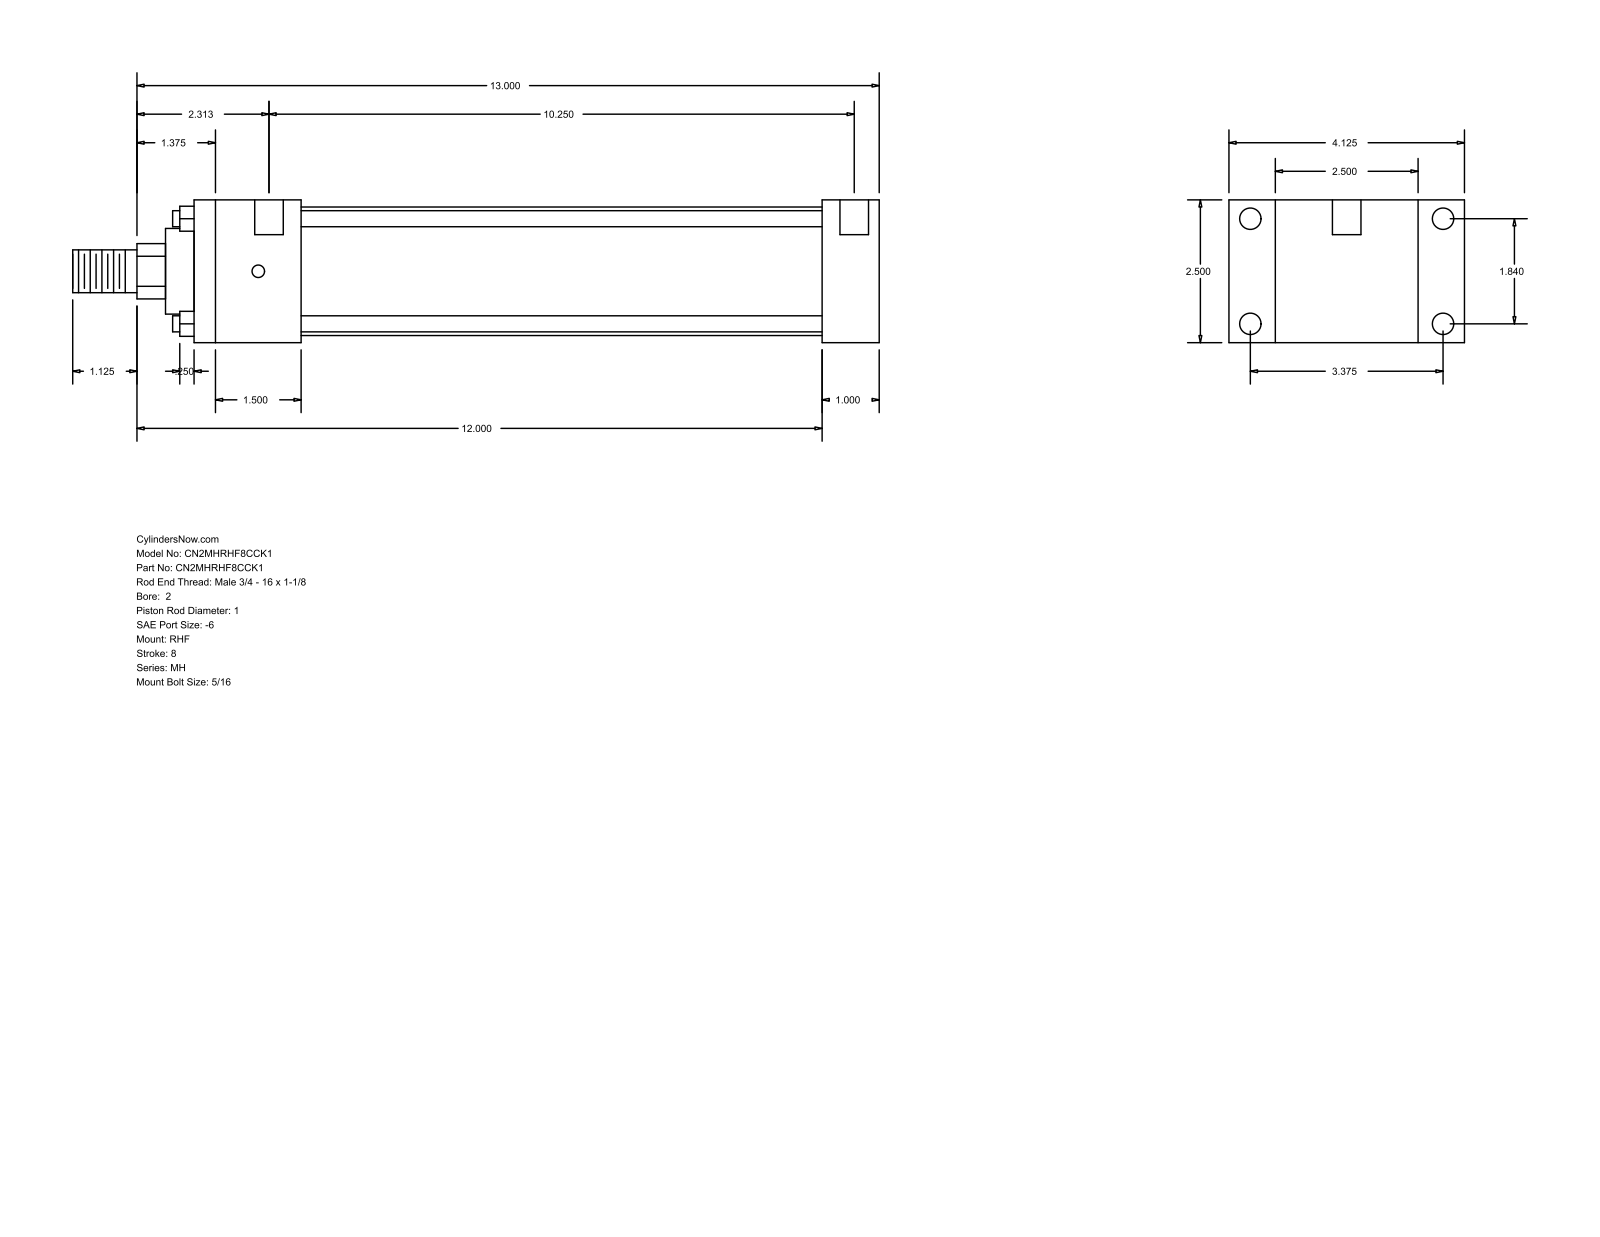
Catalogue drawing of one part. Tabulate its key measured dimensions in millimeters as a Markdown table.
| quantity | value |
| --- | --- |
| part name | MH_RHF__0200_1 |
| STEP written by | GSSL Pune (CONFIG_CONTROL_DESIGN) |
| units | millimeters |
| bodies | 0 solids, 88 faces (60 planar, 28 cylindrical, 0 other) |
| overall size | 358.77 × 104.78 × 63.5 |
| round holes (diameter × count) | 5.56 × 4, 9.53 × 4, 12.7 × 2 |
| round bosses / shafts (diameter × count) | 7.14 × 4, 57.15 × 1, 38.1 × 1, 25.4 × 1, 19.05 × 1 |
| partial cylindrical surfaces (radius × count) | 12.29 × 1 |
| main face-to-face distances | 63.5, 25.4, 20.64, 84.14, 304.8, 279.4, 104.78, 47.63, 231.77, 257.17 |
| hole center spacings | 46.74, 85.72, 97.63, 268.28, 3.17, 4.76, 260.35, 263.52 |
